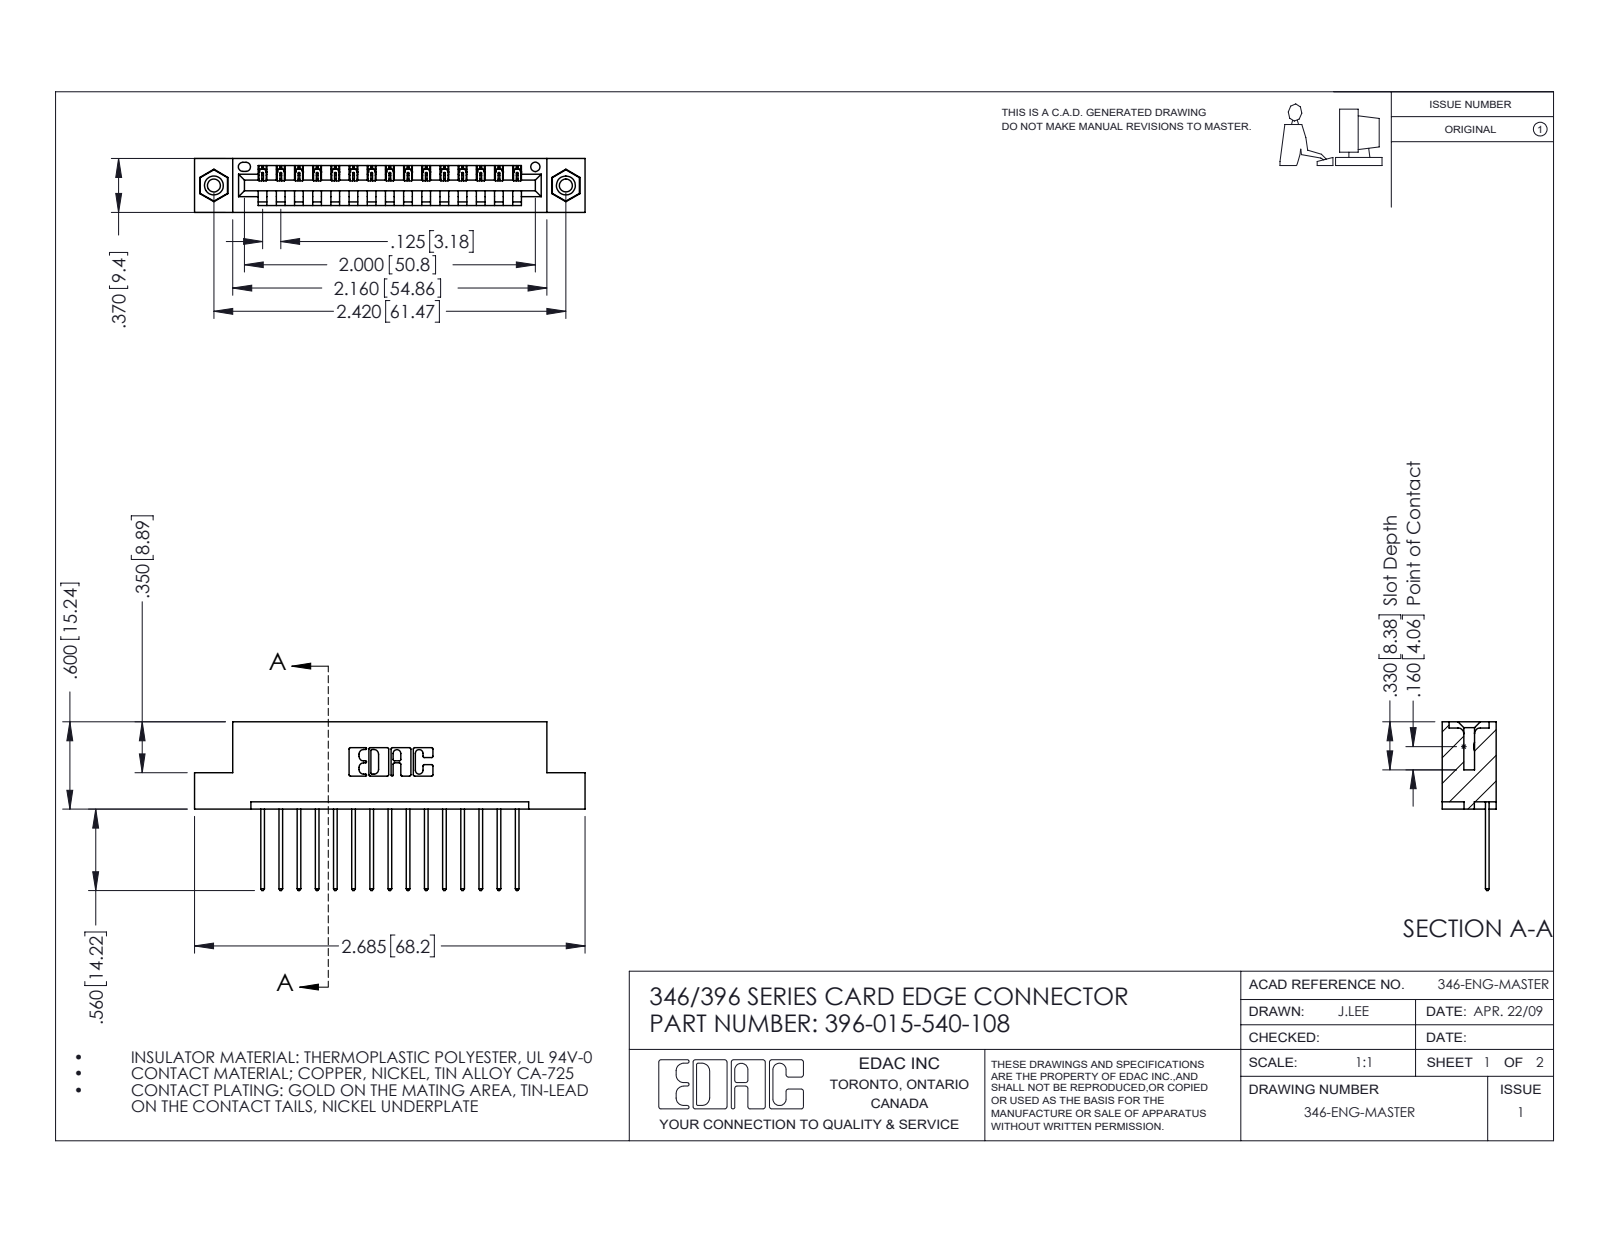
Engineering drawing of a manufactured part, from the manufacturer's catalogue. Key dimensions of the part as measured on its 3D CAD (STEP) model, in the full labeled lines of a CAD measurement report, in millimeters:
Part name (STEP PRODUCT): 346 Part_Flush Mounting Lugs - 0.156 Dia-TI; 345-292-001_345-293-140; 345-250-001_345-250-003-102; 396-015-540-108
STEP written by: SolidWorks 2016 (CONFIG_CONTROL_DESIGN)
Units: millimetres
Bodies: 18 solids, 1052 faces (708 planar, 328 cylindrical, 16 other)
Overall size (bounding box): 68.2 × 29.5 × 9.4
Volume: 6 360 mm³ · Surface area: 7 826 mm²
Round holes (diameter × count): ⌀2.3 ×2, ⌀3.2 ×2, ⌀4 ×2, ⌀1.6 ×1
Round bosses / shafts (diameter × count): ⌀3.9 ×2
Partial cylindrical surfaces — rounded edges, fillets, slot ends (radius × count): R0.2 ×30, R0.3 ×30, R0.3 ×22, R0.2 ×6, R0.8 ×6, R0.7 ×3, R0.8 ×2, R1 ×2
Main face-to-face distances: 1.2, 8.2, 6.4, 9.4, 1.8, 7.6, 0.6, 3.8, 5.6, 2.5
Hole centre spacings: 6.2, 56.2, 61.5
